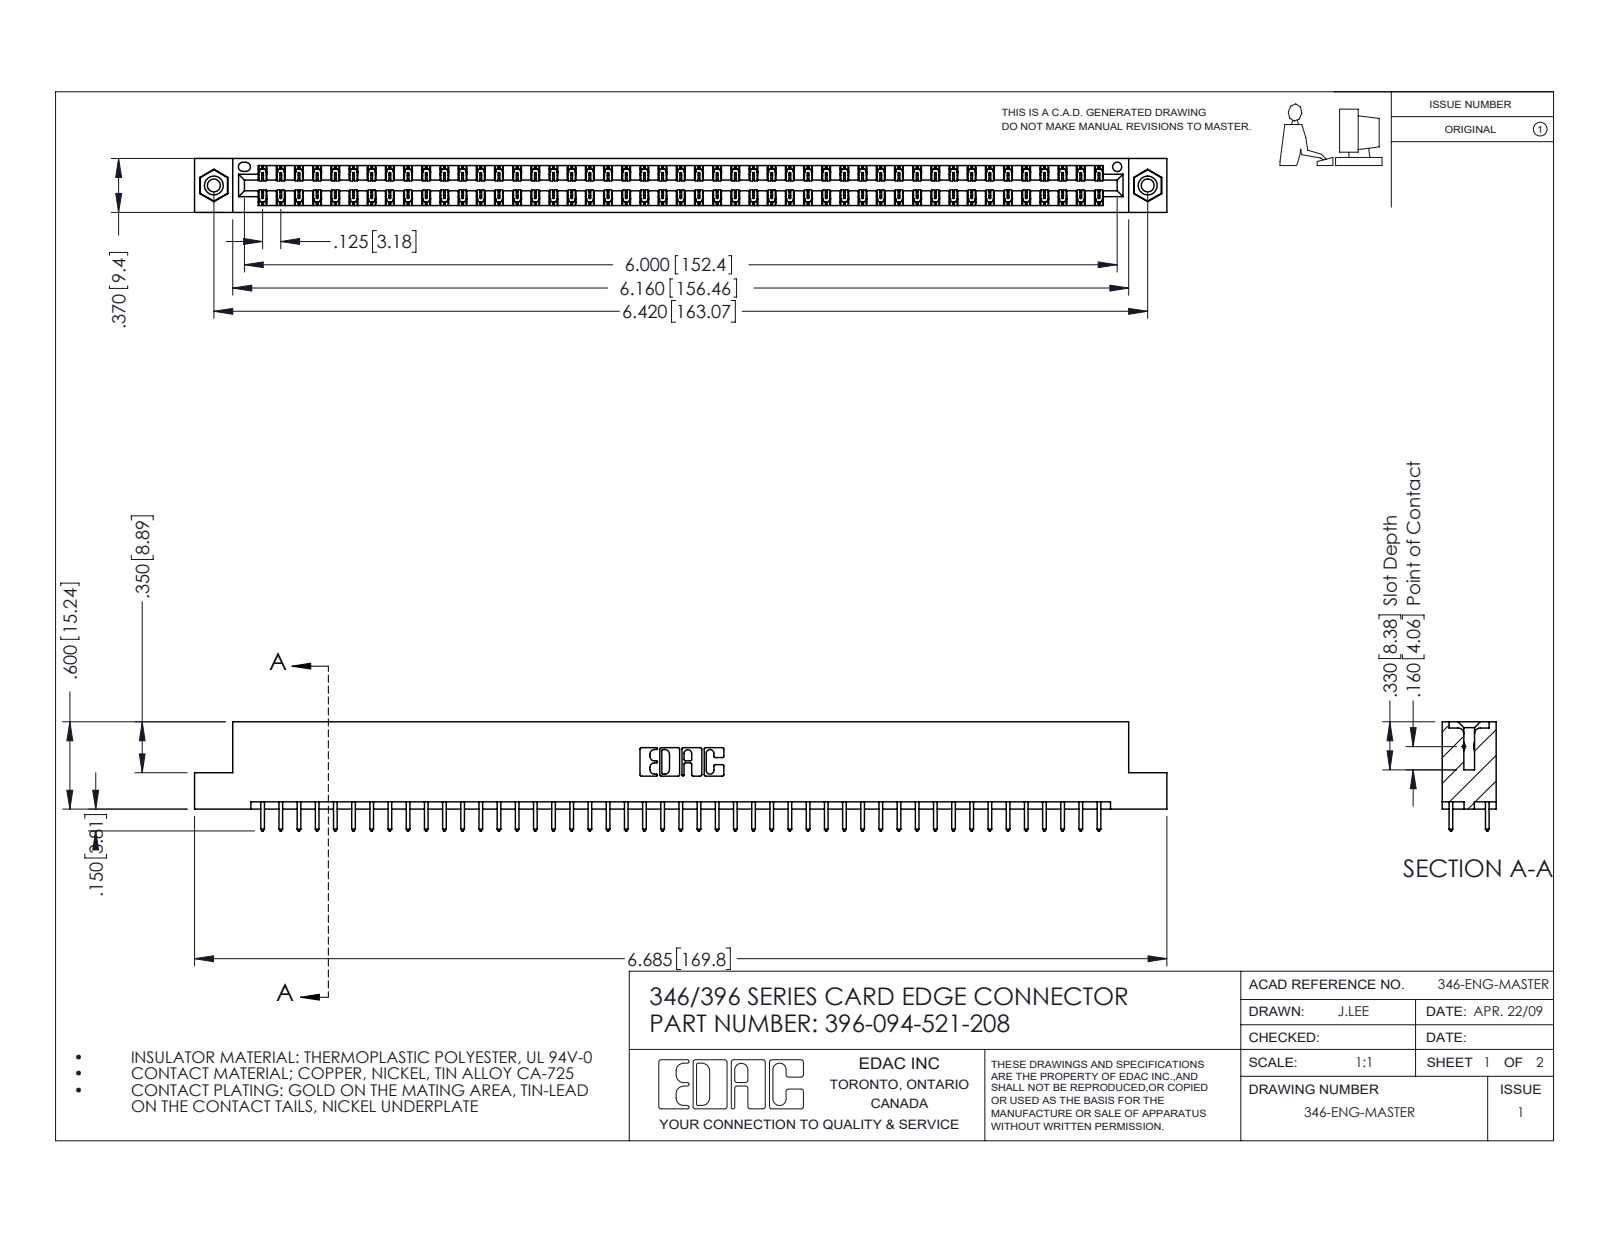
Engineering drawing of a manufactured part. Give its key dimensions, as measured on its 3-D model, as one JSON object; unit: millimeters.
{"part_name": "345-292-001_345-293-121; 345-250-001_345-250-003-102; 396-094-521-208; 346 Part_Flush Mounting Lugs - 0.156 Dia-TI", "step_written_by": "SolidWorks 2016 (CONFIG_CONTROL_DESIGN)", "units": "millimeters", "bodies": {"solids": 97, "faces": 5070, "planar": 3398, "cylindrical": 1656, "other": 16}, "overall_size": [169.8, 19.1, 9.4], "volume_mm3": 16550, "surface_area_mm2": 22590, "round_holes": [[2.3, 2], [3.2, 2], [4, 2], [1.6, 1]], "round_bosses_or_shafts": [[3.9, 2]], "partial_cylinders_radius": [[0.2, 141], [0.3, 94], [0.3, 22], [0.2, 6], [0.8, 6], [0.7, 3], [0.4, 2], [0.6, 2]], "face_to_face_distances": [1.2, 8.2, 6.4, 9.4, 1.8, 7.6, 0.6, 7, 3.8, 5.6], "hole_center_spacings": [6.2, 157.8, 163.1]}
